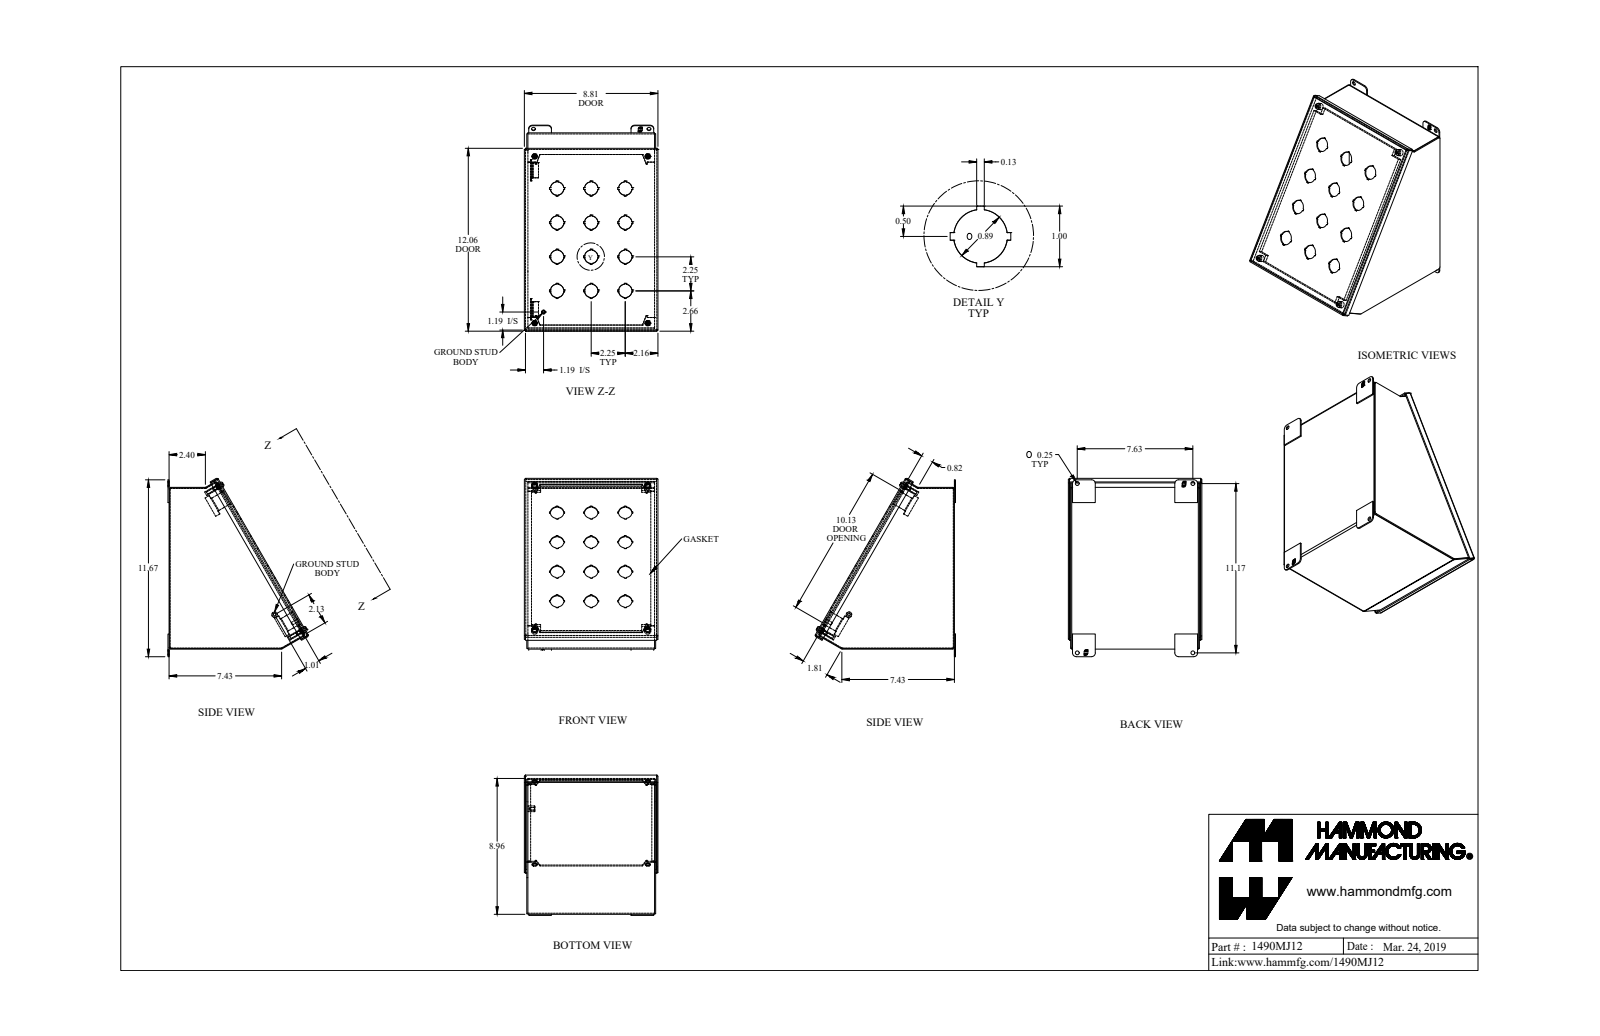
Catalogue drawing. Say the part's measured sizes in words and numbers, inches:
The part is named "1490MJ12_Default". Its 3-D file was written by "SolidWorks 2019 (CONFIG_CONTROL_DESIGN)". It is 26 solids with 885 faces: 627 planar, 220 cylindrical and 38 other. Overall it measures 11.788 by 9.303 by 8.812 inches. Its volume is 33.56 cubic inches and its surface area 956.4 square inches. Round holes: 8 of diameter 0.25, 8 of diameter 0.875, 4 of diameter 0.159, 4 of diameter 0.875, 1 of diameter 0.12, 1 of diameter 0.136, 1 of diameter 0.156. Round bosses or shafts: 4 of diameter 0.39, 4 of diameter 0.275, 4 of diameter 0.19, 4 of diameter 0.148, 1 of diameter 0.375, 1 of diameter 0.29. Partial cylindrical surfaces (rounded edges, fillets, slot ends): 18 of radius 0.108, 12 of radius 0.036, 9 of radius 0.029, 9 of radius 0.086, 8 of radius 0.25, 4 of radius 0.125, 4 of radius 0.16, 4 of radius 0.171. The main face-to-face distances are 0.072, 8.428, 8.356, 8.5, 10.595, 10.667, 10.523, 0.222, 11.678, 0.163. The hole center spacings are 2.25, 5.031, 3.182, 4.5, 7.409, 4.293, 4.619, 5.749.
